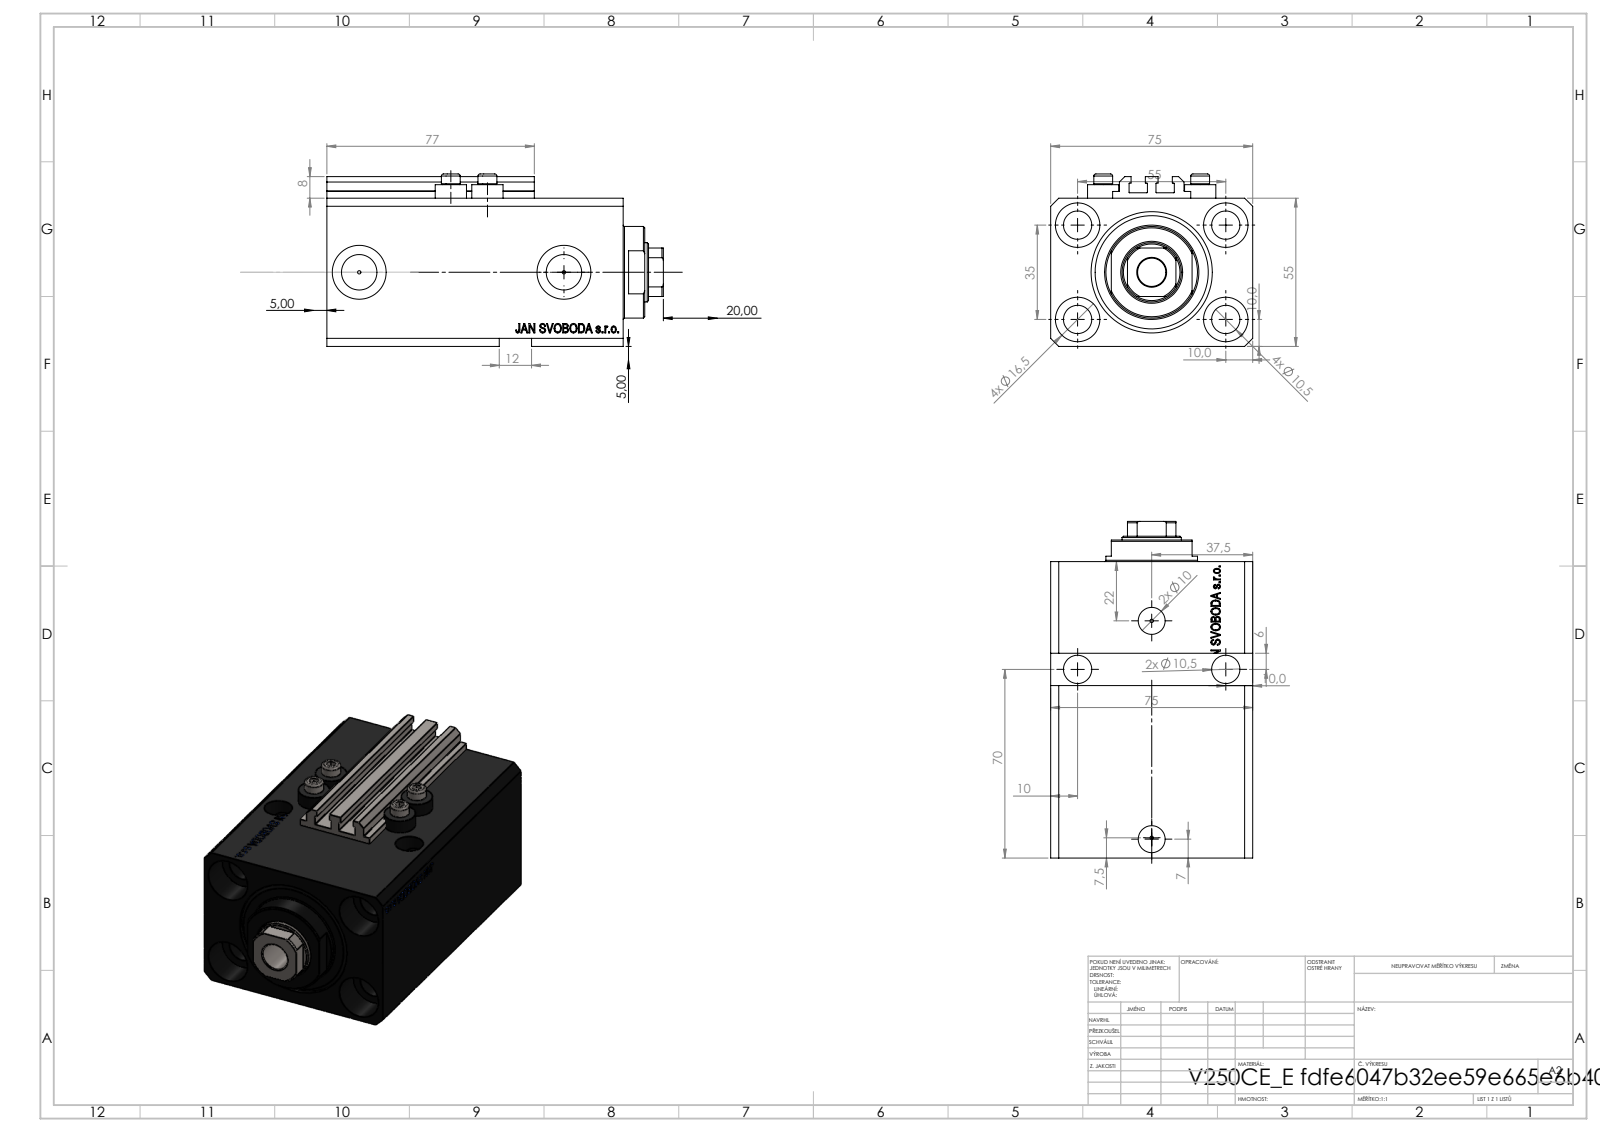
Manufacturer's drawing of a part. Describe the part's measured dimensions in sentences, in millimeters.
The part is named "V250CE_E_Body; V250CE_VC_E; V250CE_C_VCP; ALLEN BOLT V250CE". Its 3-D file was written by "SolidWorks 2019 (CONFIG_CONTROL_DESIGN)". It is 8 solids with 1084 faces: 514 planar, 146 cylindrical and 424 other. Overall it measures 125 by 75 by 64 millimeters. Its volume is 381 338 cubic millimeters and its surface area 95 642 square millimeters. Round holes: 9 of diameter 10.5, 4 of diameter 1.25, 4 of diameter 4, 4 of diameter 16.5, 2 of diameter 10, 2 of diameter 13.16, 2 of diameter 20, 1 of diameter 22, 1 of diameter 32, 1 of diameter 45. Round bosses or shafts: 4 of diameter 11.6, 4 of diameter 7, 1 of diameter 34. Partial cylindrical surfaces (rounded edges, fillets, slot ends): 10 of radius 0.2, 1 of radius 10.5. The main face-to-face distances are 55, 75, 15, 110, 95, 3, 9.9, 85.1, 100.1, 57. The hole center spacings are 32.6, 32.87, 55, 68.74, 13.6, 14.09, 23.05, 25.81.
